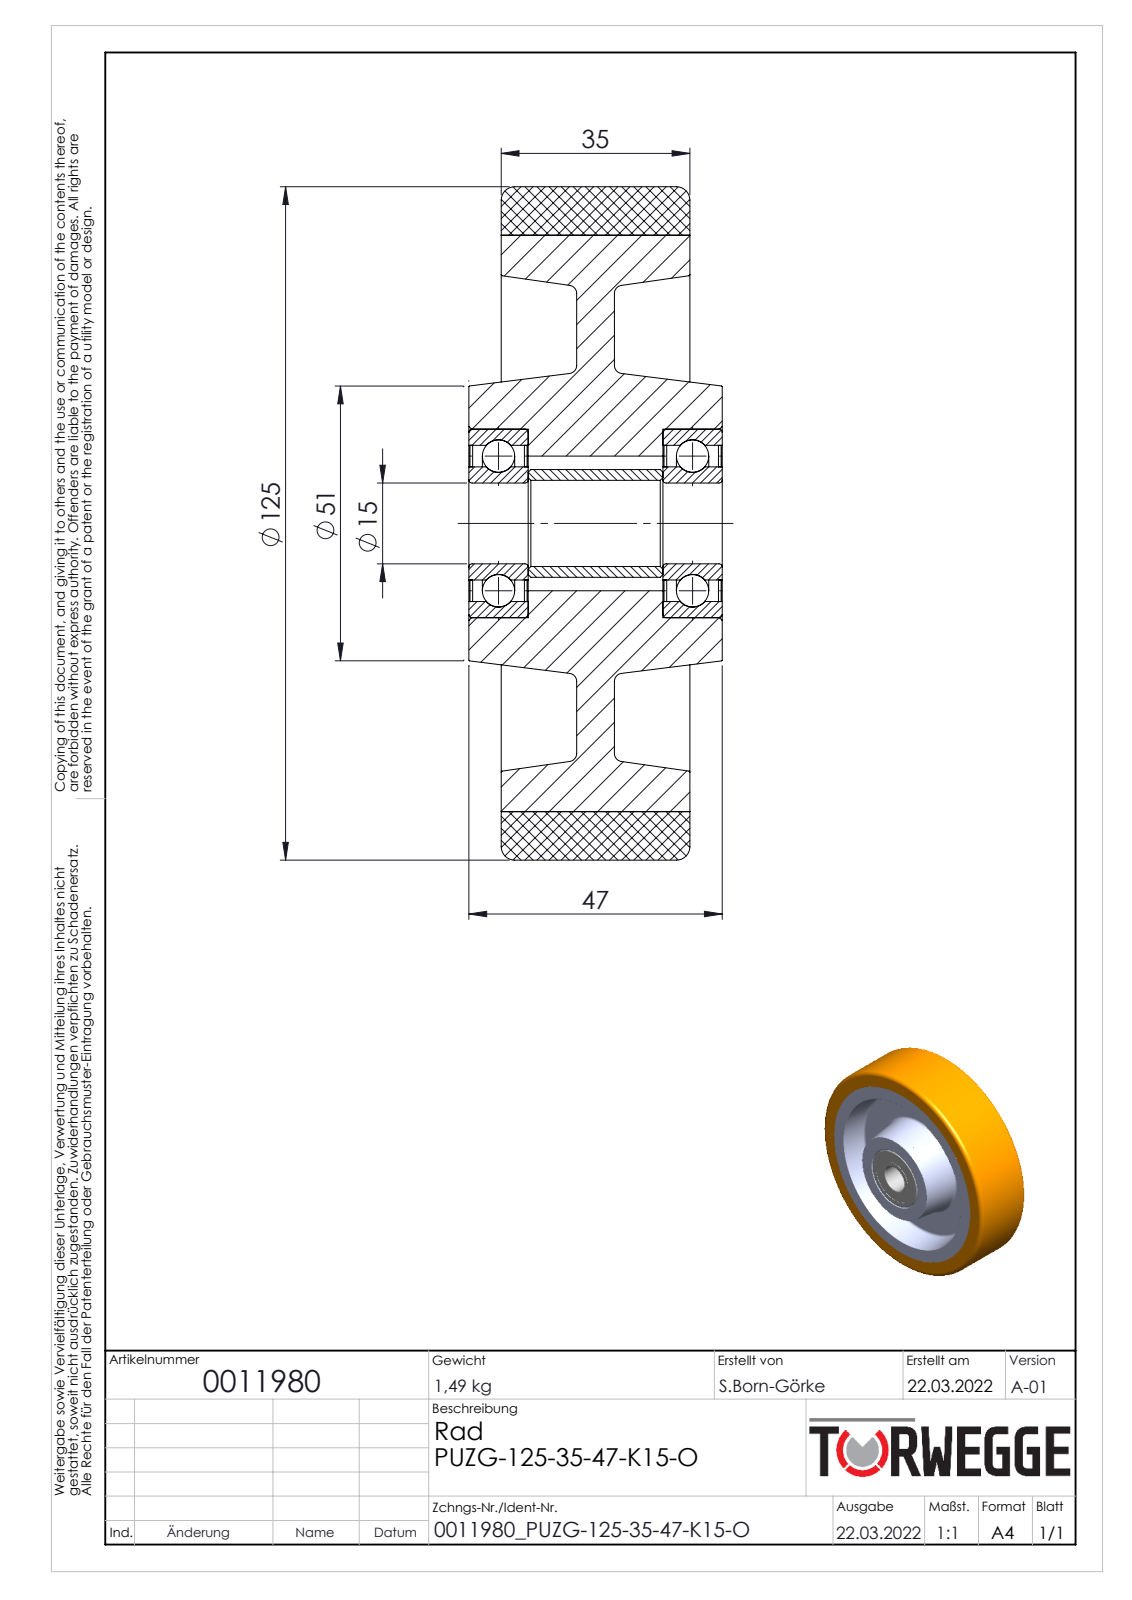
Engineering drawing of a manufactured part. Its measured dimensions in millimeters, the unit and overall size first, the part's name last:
Units: millimetres
Overall size (bounding box): 125 × 125 × 47
Round holes (diameter × count): ⌀15 ×1, ⌀16 ×1, ⌀21 ×1, ⌀25 ×1, ⌀29 ×1, ⌀35 ×1, ⌀107 ×1
Round bosses / shafts (diameter × count): ⌀125 ×1, ⌀20 ×1
Main face-to-face distances: 14, 21, 35, 36, 7, 6, 20, 27, 41, 11
Volume: 324 278 mm³ · Surface area: 94 237 mm²
Bodies: 13 solids, 160 faces (28 planar, 56 cylindrical, 76 other)
Part name (STEP PRODUCT): 0011980
STEP written by: SolidWorks 2020 (AUTOMOTIVE_DESIGN)
